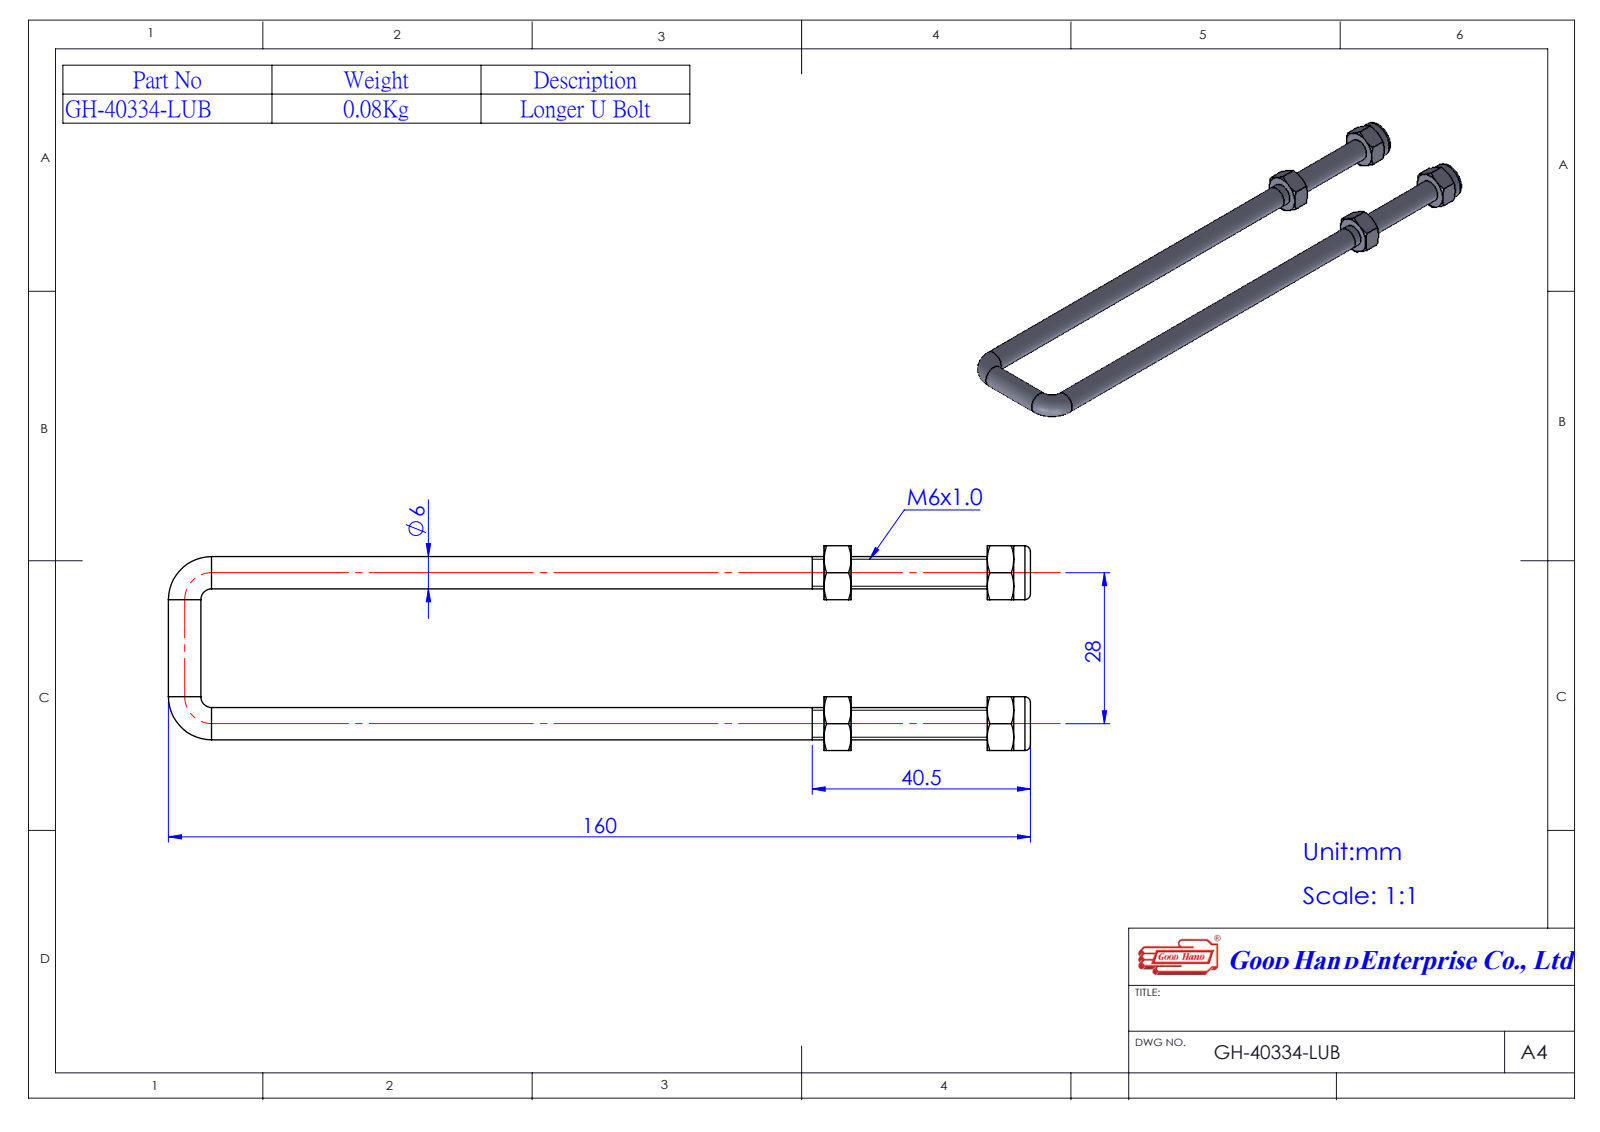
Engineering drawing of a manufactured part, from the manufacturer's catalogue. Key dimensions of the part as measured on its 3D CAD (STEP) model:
Part name (STEP PRODUCT): 44033444LUB; prevailing torque nut style 1 insert_DIN_DIN EN ISO 7040 - M6 - N; Hexagon Nut_2_JIS_JIS B 1181 Hexagon nut - Class 2 Finished M6 --C; GH-40334-LUB
STEP written by: SolidWorks 2016 (AUTOMOTIVE_DESIGN)
Units: millimetres
Bodies: 5 solids, 146 faces (36 planar, 34 cylindrical, 76 other)
Overall size (bounding box): 160 × 38 × 11.55
Volume: 11 161 mm³ · Surface area: 8 167 mm²
Round holes (diameter × count): ⌀5 ×2, ⌀6 ×2, ⌀7.14 ×2
Round bosses / shafts (diameter × count): ⌀10 ×2, ⌀6 ×1
Main face-to-face distances: 10, 14, 28, 24, 4, 5, 30.3, 25.3, 38.3, 33.3
Hole centre spacings: 28
